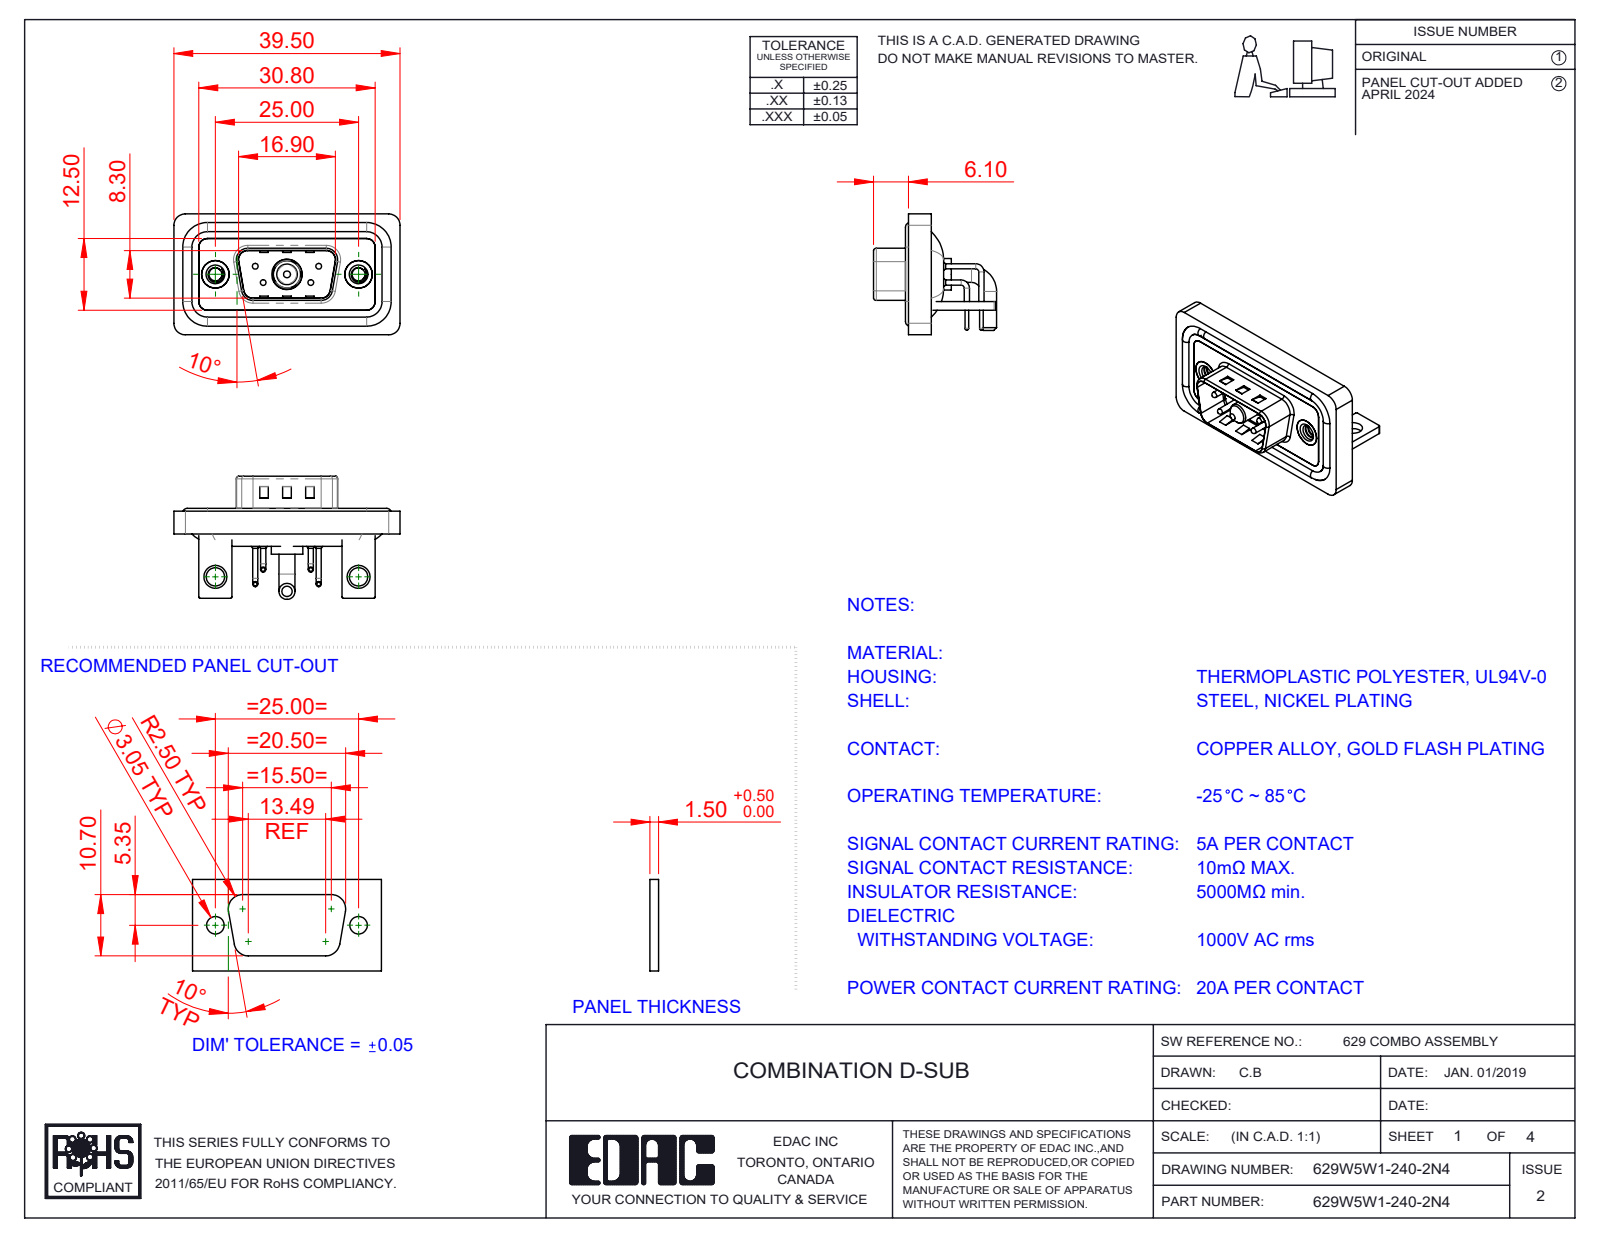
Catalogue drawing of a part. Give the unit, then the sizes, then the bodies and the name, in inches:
Units: inches
Overall size (bounding box): 1.555 × 0.846 × 0.831
Round holes (diameter × count): ⌀0.03 ×4, ⌀0.063 ×4, ⌀0.079 ×4, ⌀0.089 ×2, ⌀0.126 ×2, ⌀0.157 ×2, ⌀0.189 ×2, ⌀0.197 ×2, ⌀0.191 ×1, ⌀0.209 ×1
Round bosses / shafts (diameter × count): ⌀0.035 ×8, ⌀0.063 ×4, ⌀0.059 ×4, ⌀0.039 ×4, ⌀0.026 ×4, ⌀0.193 ×2, ⌀0.11 ×2, ⌀0.217 ×1
Partial cylindrical surfaces — rounded edges, fillets, slot ends (radius × count): R0.079 ×19, R0.059 ×18, R0.01 ×16, R0.02 ×9, R0.063 ×8, R0.024 ×4, R0.026 ×4, R0.035 ×4
Main face-to-face distances: 0.016, 0.059, 0.031, 0.114, 0.043, 0.083, 0.047, 0.063, 0.098, 0.146
Hole centre spacings: 0.124, 0.225, 0.28, 0.492, 0.713, 0.984, 0.173, 0.173
Volume: 0.29 in³ · Surface area: 12.01 in²
Bodies: 15 solids, 934 faces (431 planar, 363 cylindrical, 140 other)
Part name (STEP PRODUCT): 629Combo Waterproof Housing_09 Contacts; 629Combo Threaded Rivet_3; 629Combo Shell Front_09 Contacts; 629Combo Shell Rear_09 Contacts (+6 more)
STEP written by: SolidWorks 2023 (CONFIG_CONTROL_DESIGN)
